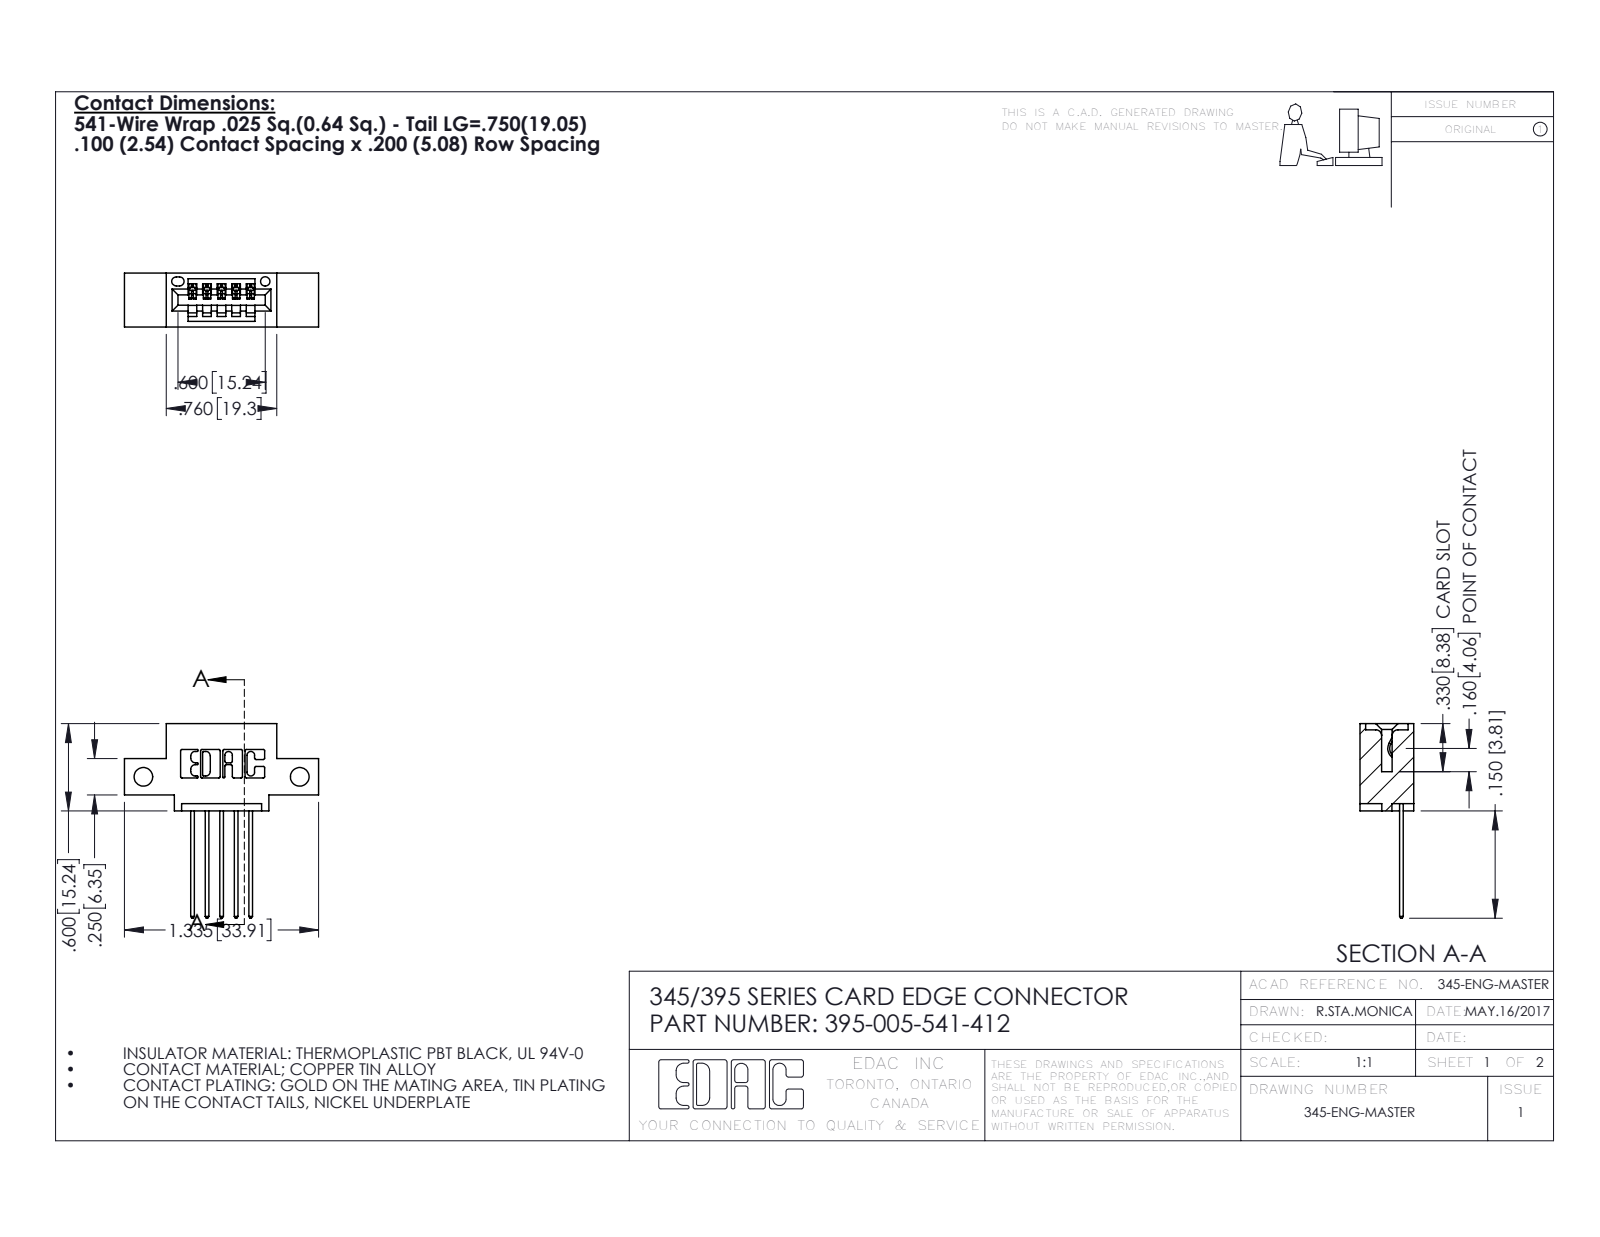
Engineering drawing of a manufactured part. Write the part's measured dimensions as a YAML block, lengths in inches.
part_name: "345 Part_0.110 Offset - Side Mount; 395-005-541-412; 345-292-001_345-293-141"
step_written_by: "SolidWorks 2016 (CONFIG_CONTROL_DESIGN)"
units: inches
bodies: {solids: 6, faces: 420, planar: 284, cylindrical: 136, other: 0}
overall_size: [1.337, 1.335, 0.37]
volume: 0.169
surface_area: 4.991
round_holes:
  - {diameter: 0.128, count: 2}
  - {diameter: 0.064, count: 1}
partial_cylinders:
  - {radius: 0.01, count: 22}
  - {radius: 0.006, count: 10}
  - {radius: 0.01, count: 10}
  - {radius: 0.007, count: 6}
  - {radius: 0.031, count: 6}
  - {radius: 0.026, count: 3}
  - {radius: 0.031, count: 2}
  - {radius: 0.04, count: 2}
face_to_face_distances: [0.2, 0.37, 0.298, 0.072, 0.1, 0.025, 0.098, 0.272, 0.25, 0.06]
hole_center_spacings: [1.075]
